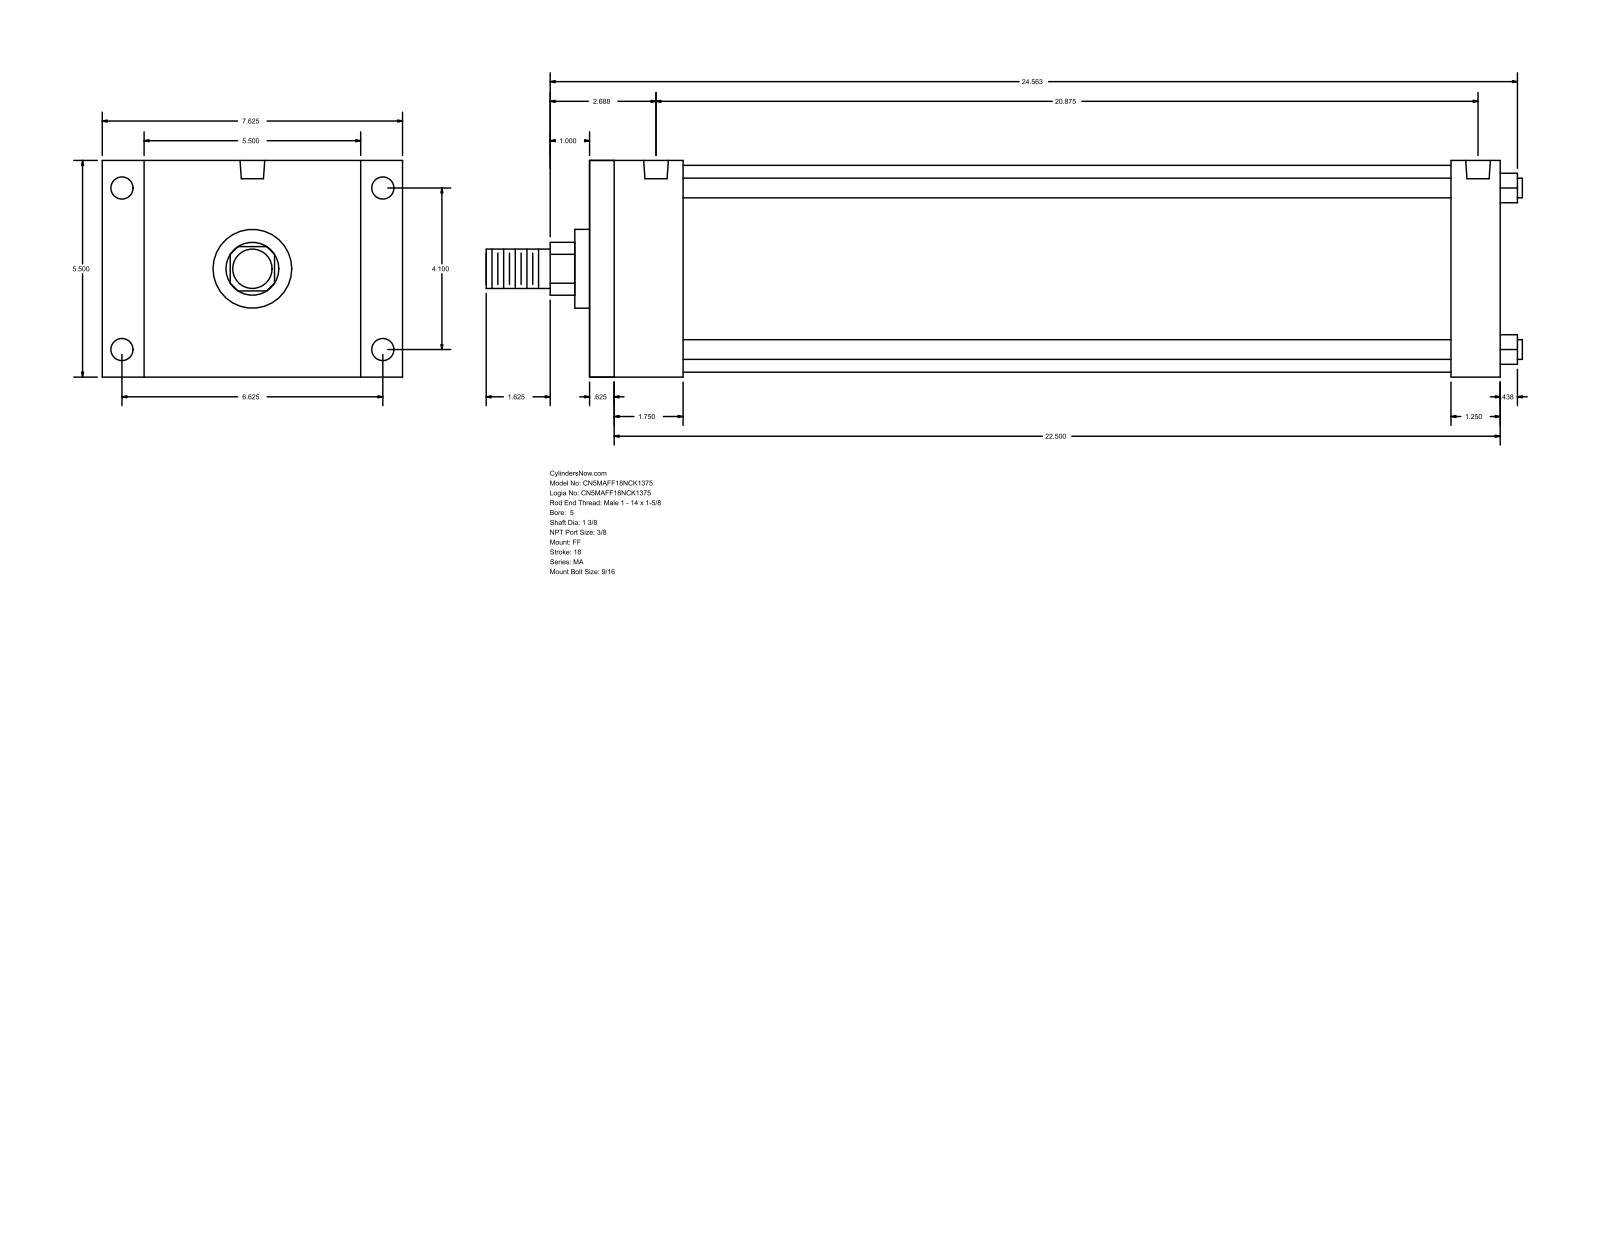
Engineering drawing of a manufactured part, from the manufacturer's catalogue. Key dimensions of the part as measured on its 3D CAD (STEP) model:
Part name (STEP PRODUCT): MA_FF__0500_1.375
STEP written by: GSSL Pune (CONFIG_CONTROL_DESIGN)
Units: millimetres
Bodies: 0 solids, 92 faces (64 planar, 28 cylindrical, 0 other)
Overall size (bounding box): 668.34 × 193.68 × 139.7
Round holes (diameter × count): ⌀11.11 ×4, ⌀14.29 ×4, ⌀15.93 ×2
Round bosses / shafts (diameter × count): ⌀12.7 ×4, ⌀133.35 ×1, ⌀50.8 ×1, ⌀34.92 ×1, ⌀25.4 ×1
Partial cylindrical surfaces — rounded edges, fillets, slot ends (radius × count): R17.06 ×1
Main face-to-face distances: 139.7, 587.37, 15.87, 571.5, 555.62, 539.75, 31.75, 60.32, 44.45, 495.3
Hole centre spacings: 104.14, 168.28, 197.9, 520.7, 4.76, 4.77, 525.46, 525.47
